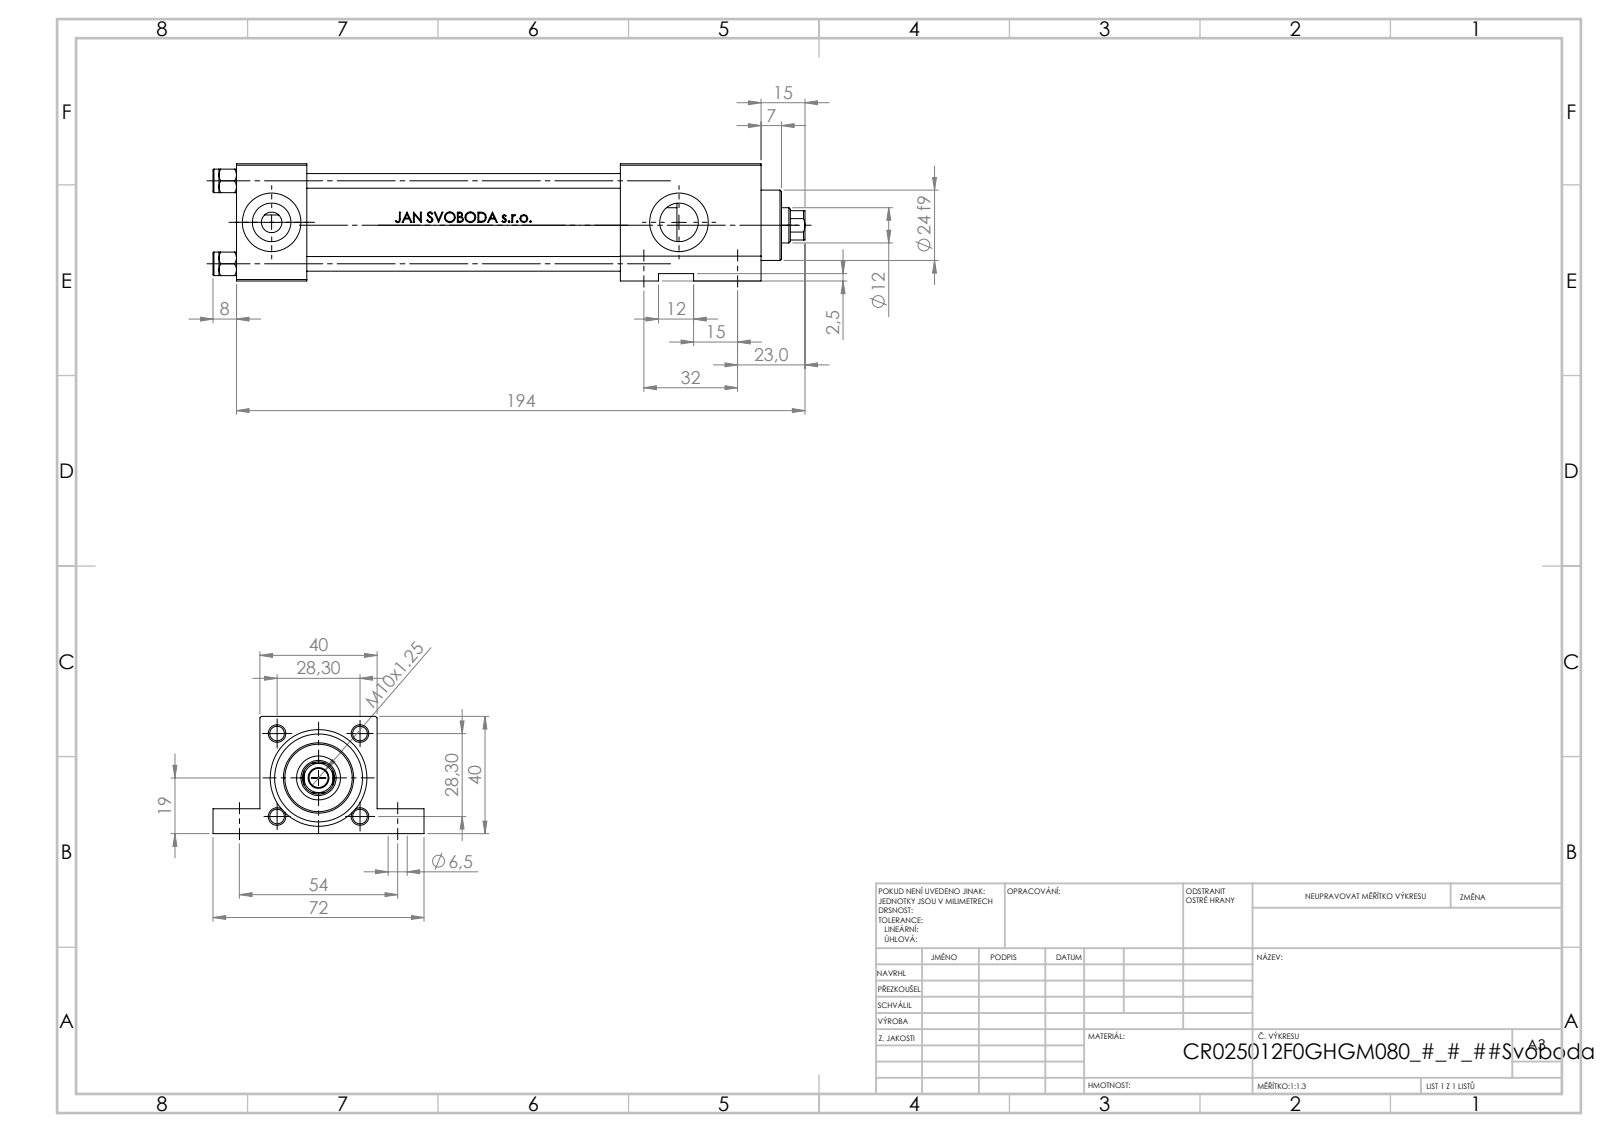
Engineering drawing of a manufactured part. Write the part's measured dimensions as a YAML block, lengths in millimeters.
part_name: "V215CR_F_TYCINKA; V215_VC_A; V215CR_VCP_F; V215CR_F_Body (+1 more)"
step_written_by: "SolidWorks 2019 (CONFIG_CONTROL_DESIGN)"
units: millimeters
bodies: {solids: 11, faces: 1102, planar: 436, cylindrical: 126, other: 540}
overall_size: [202, 72, 40]
volume: 179854
surface_area: 75031
round_holes:
  - {diameter: 6.5, count: 5}
  - {diameter: 5, count: 4}
  - {diameter: 20, count: 3}
  - {diameter: 7, count: 2}
  - {diameter: 13.16, count: 2}
  - {diameter: 12, count: 1}
  - {diameter: 15, count: 1}
  - {diameter: 25, count: 1}
  - {diameter: 30, count: 1}
round_bosses_or_shafts:
  - {diameter: 8, count: 4}
  - {diameter: 31, count: 1}
  - {diameter: 24, count: 1}
partial_cylinders:
  - {radius: 5.5, count: 1}
face_to_face_distances: [40, 24, 8.5, 31.5, 48, 131, 107, 179, 155, 19.3]
hole_center_spacings: [28.3, 19.32, 20.73, 32, 40.02, 54, 62.77, 139]
